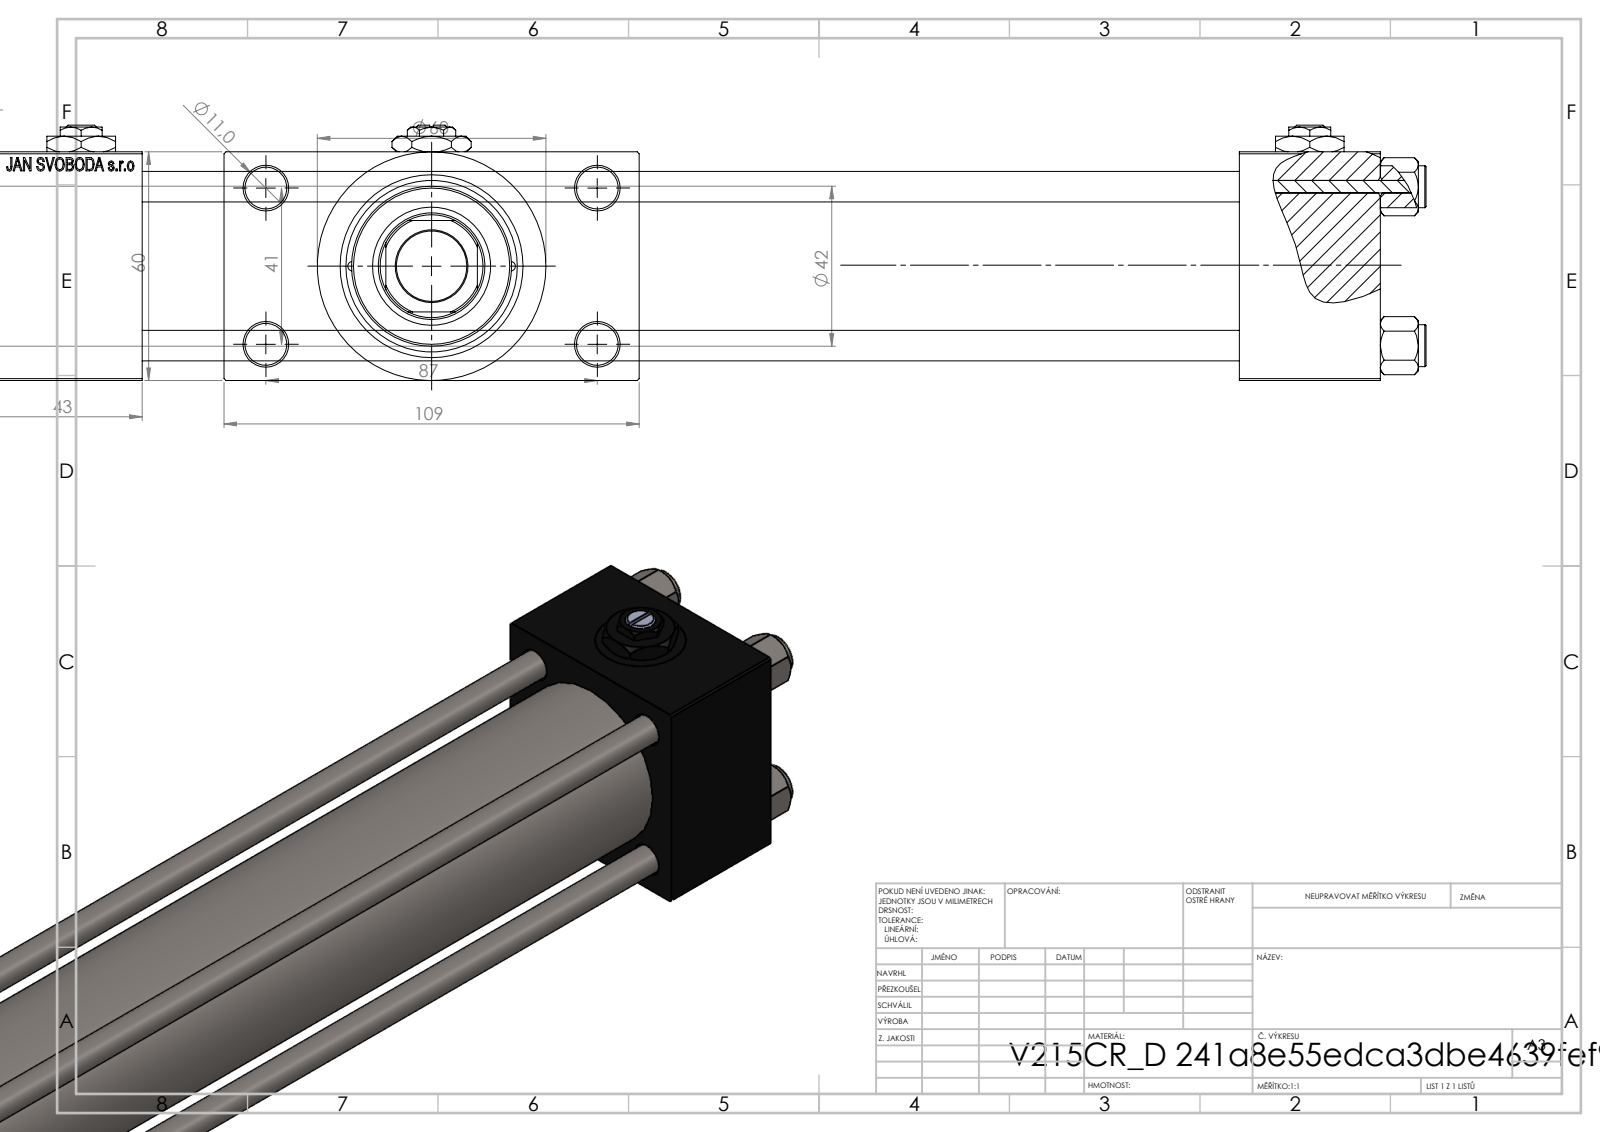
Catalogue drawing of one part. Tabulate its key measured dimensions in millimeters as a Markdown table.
| quantity | value |
| --- | --- |
| part name | V215CR_D_Body; NUT_M5_D; V215_VC_A; Zatka_pro_OIL_PORT (+2 more) |
| STEP written by | SolidWorks 2019 (CONFIG_CONTROL_DESIGN) |
| units | millimeters |
| bodies | 13 solids, 1215 faces (550 planar, 103 cylindrical, 562 other) |
| overall size | 415 × 109 × 67 |
| volume | 807 558 mm³ |
| surface area | 237 216 mm² |
| round holes (diameter × count) | 8 × 4, 11 × 4, 16.66 × 4, 24 × 4, 7 × 3, 2.5 × 2, 18.5 × 1, 28 × 1, 31 × 1, 40 × 1, 45 × 1 |
| round bosses / shafts (diameter × count) | 11 × 4, 60 × 1, 46 × 1, 42 × 1 |
| partial cylindrical surfaces (radius × count) | 13.5 × 1 |
| main face-to-face distances | 60, 24.5, 288, 84.5, 37, 325, 368, 331, 43, 109 |
| hole center spacings | 20.85, 22.65, 29.49, 30.62, 41.7, 46.53, 47.15, 48.09 |
